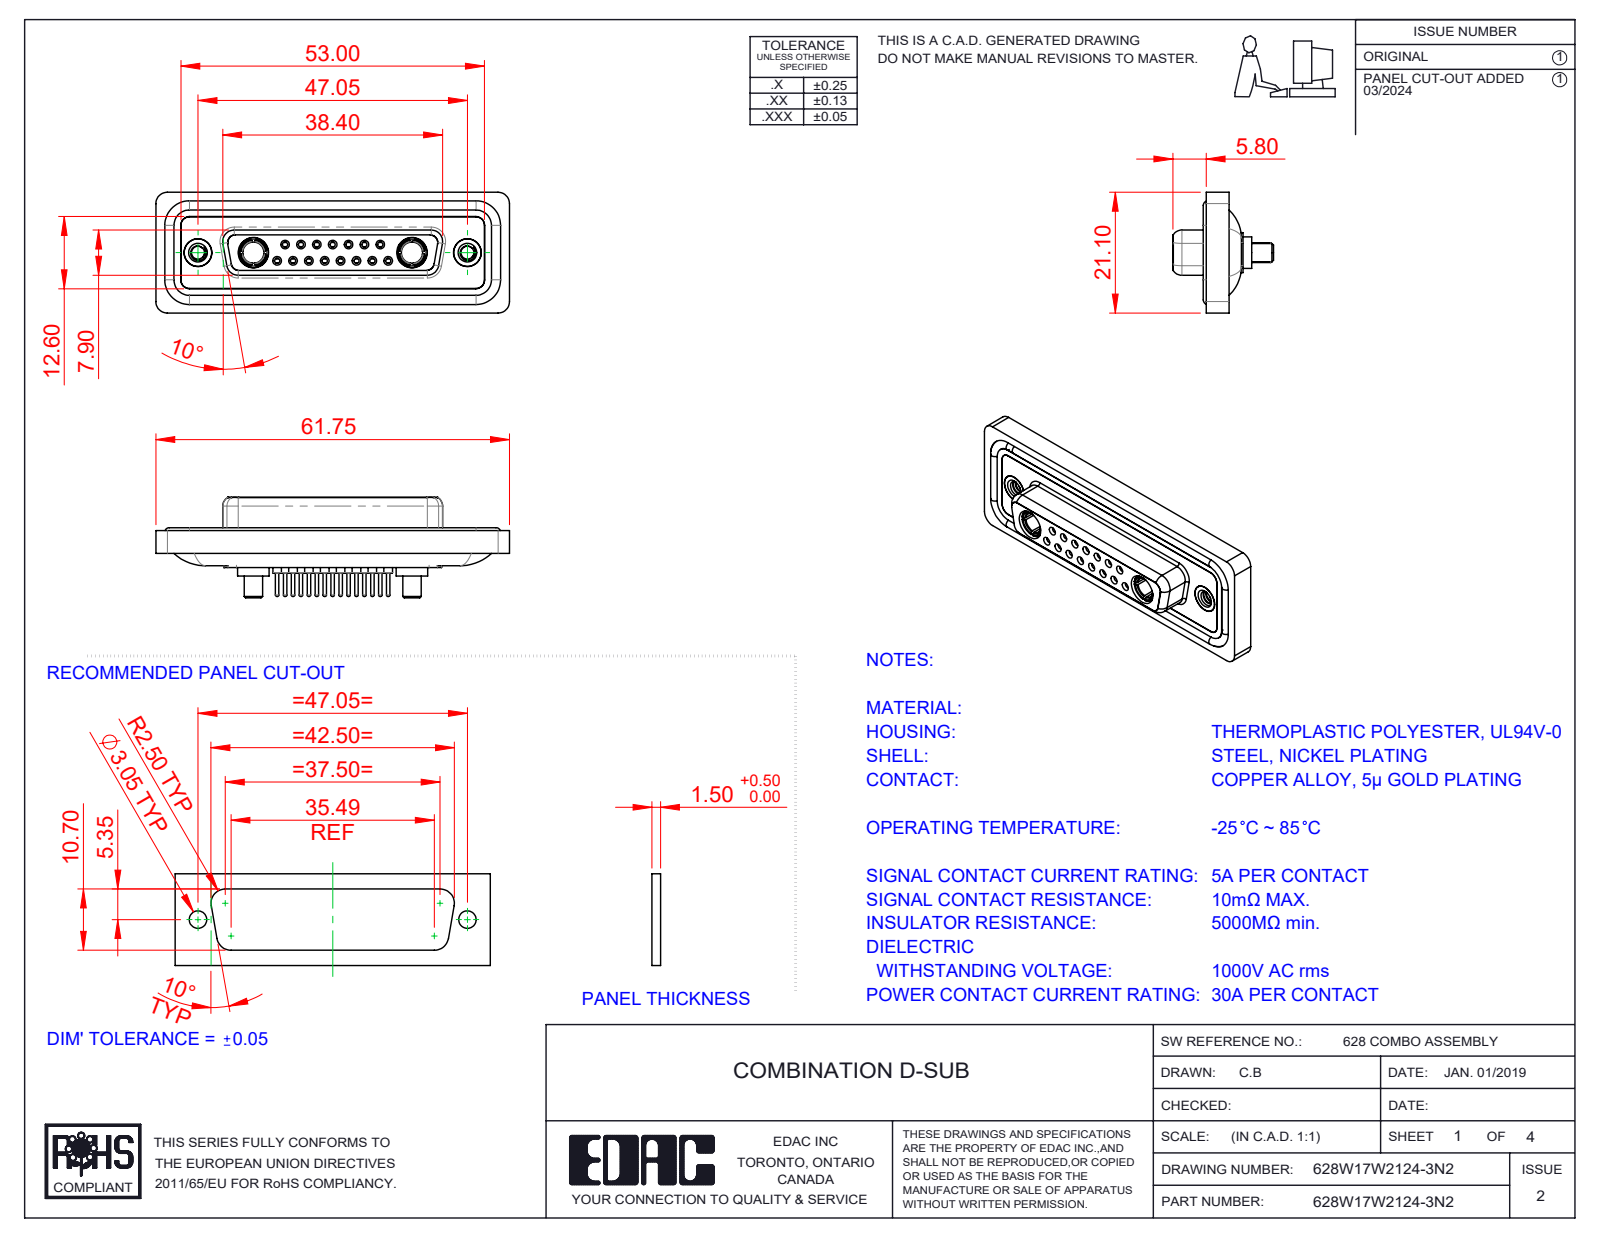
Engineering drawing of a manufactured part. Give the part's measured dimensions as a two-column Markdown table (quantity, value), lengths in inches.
| quantity | value |
| --- | --- |
| part name | 628Combo Housing_17W2; Power Socket_30A S; 628Combo Threaded Rivet_2; 628Combo Contact Row 2_24 (+5 more) |
| STEP written by | SolidWorks 2023 (CONFIG_CONTROL_DESIGN) |
| units | inches |
| bodies | 26 solids, 1359 faces (388 planar, 519 cylindrical, 452 other) |
| overall size | 2.431 × 0.831 × 0.691 |
| volume | 0.509 in³ |
| surface area | 21.49 in² |
| round holes (diameter × count) | 0.035 × 15, 0.043 × 15, 0.059 × 15, 0.079 × 15, 0.063 × 8, 0.067 × 7, 0.191 × 4, 0.089 × 2, 0.146 × 2, 0.157 × 2, 0.159 × 2, 0.197 × 2 |
| round bosses / shafts (diameter × count) | 0.087 × 15, 0.024 × 15, 0.063 × 11, 0.217 × 2, 0.205 × 2, 0.195 × 2, 0.195 × 2, 0.189 × 2 |
| partial cylindrical surfaces (radius × count) | 0.059 × 22, 0.079 × 18, 0.053 × 8, 0.063 × 8, 0.01 × 4, 0.02 × 4, 0.024 × 4, 0.026 × 4 |
| main face-to-face distances | 0.016, 0.071, 0.293, 0.222, 0.26, 0.02, 0.278, 0.063, 0.114, 0.043 |
| hole center spacings | 0.124, 0.109, 0.327, 0.218, 0.198, 0.198, 0.295, 0.436 |
